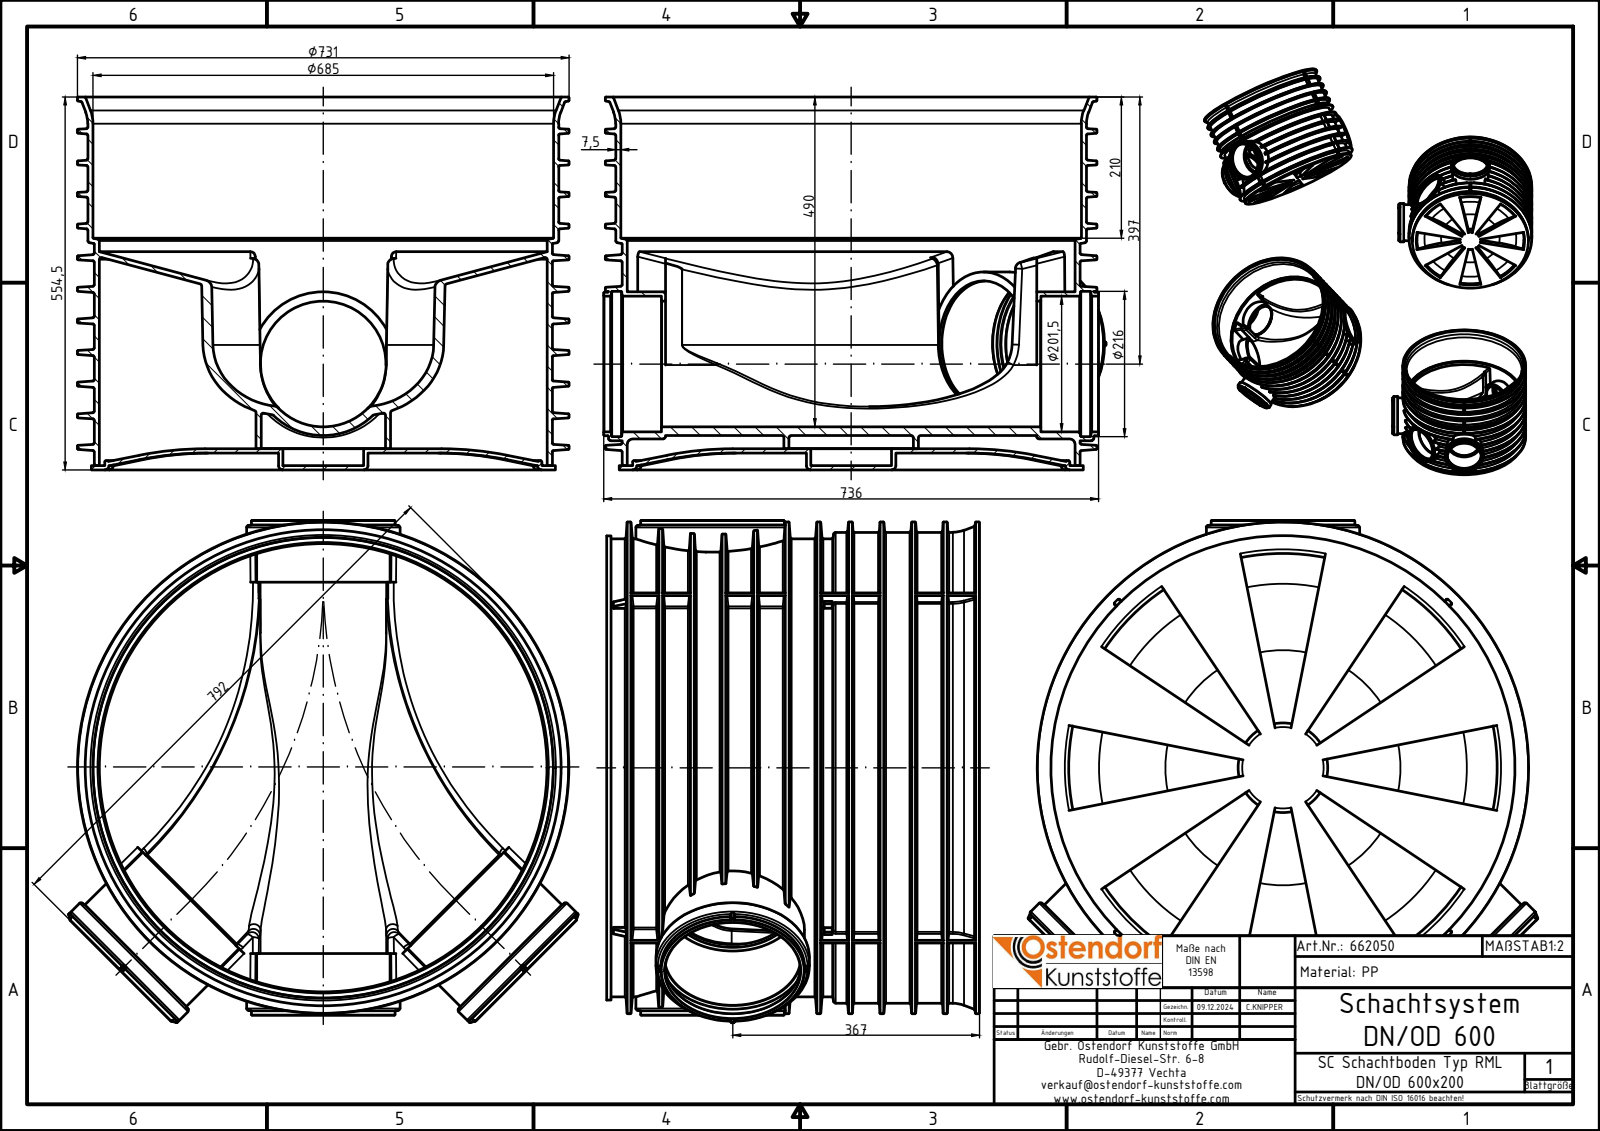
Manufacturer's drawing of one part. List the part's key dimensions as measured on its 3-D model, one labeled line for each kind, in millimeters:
Part name (STEP PRODUCT): 662050z; 662050 Schacht DN600 Boden_z; 662050 Schachtboden DN600 Grundkörper_z
STEP written by: Autodesk Inventor 2024 (AUTOMOTIVE_DESIGN)
Units: millimetres
Bodies: 2 solids, 1746 faces (190 planar, 296 cylindrical, 1260 other)
Overall size (bounding box): 757.89 × 746.94 × 554.5
Volume: 25 720 000 mm³ · Surface area: 5 603 000 mm²
Round holes (diameter × count): ⌀201.5 ×5, ⌀216 ×3, ⌀186.66 ×2, ⌀120 ×1, ⌀185 ×1, ⌀186.7 ×1, ⌀640 ×1, ⌀666 ×1, ⌀685 ×1
Round bosses / shafts (diameter × count): ⌀213.5 ×5, ⌀228 ×3, ⌀731 ×1, ⌀700 ×1, ⌀690 ×1, ⌀681 ×1, ⌀650 ×1, ⌀200 ×1
Partial cylindrical surfaces — rounded edges, fillets, slot ends (radius × count): R1 ×56, R2 ×16, R3 ×4, R106.35 ×3, R93.35 ×2, R66.5 ×1, R107.25 ×1, R111.35 ×1
Main face-to-face distances: 6.5, 25, 31.5, 18.5, 6, 554.5, 548, 529.5, 523, 13
